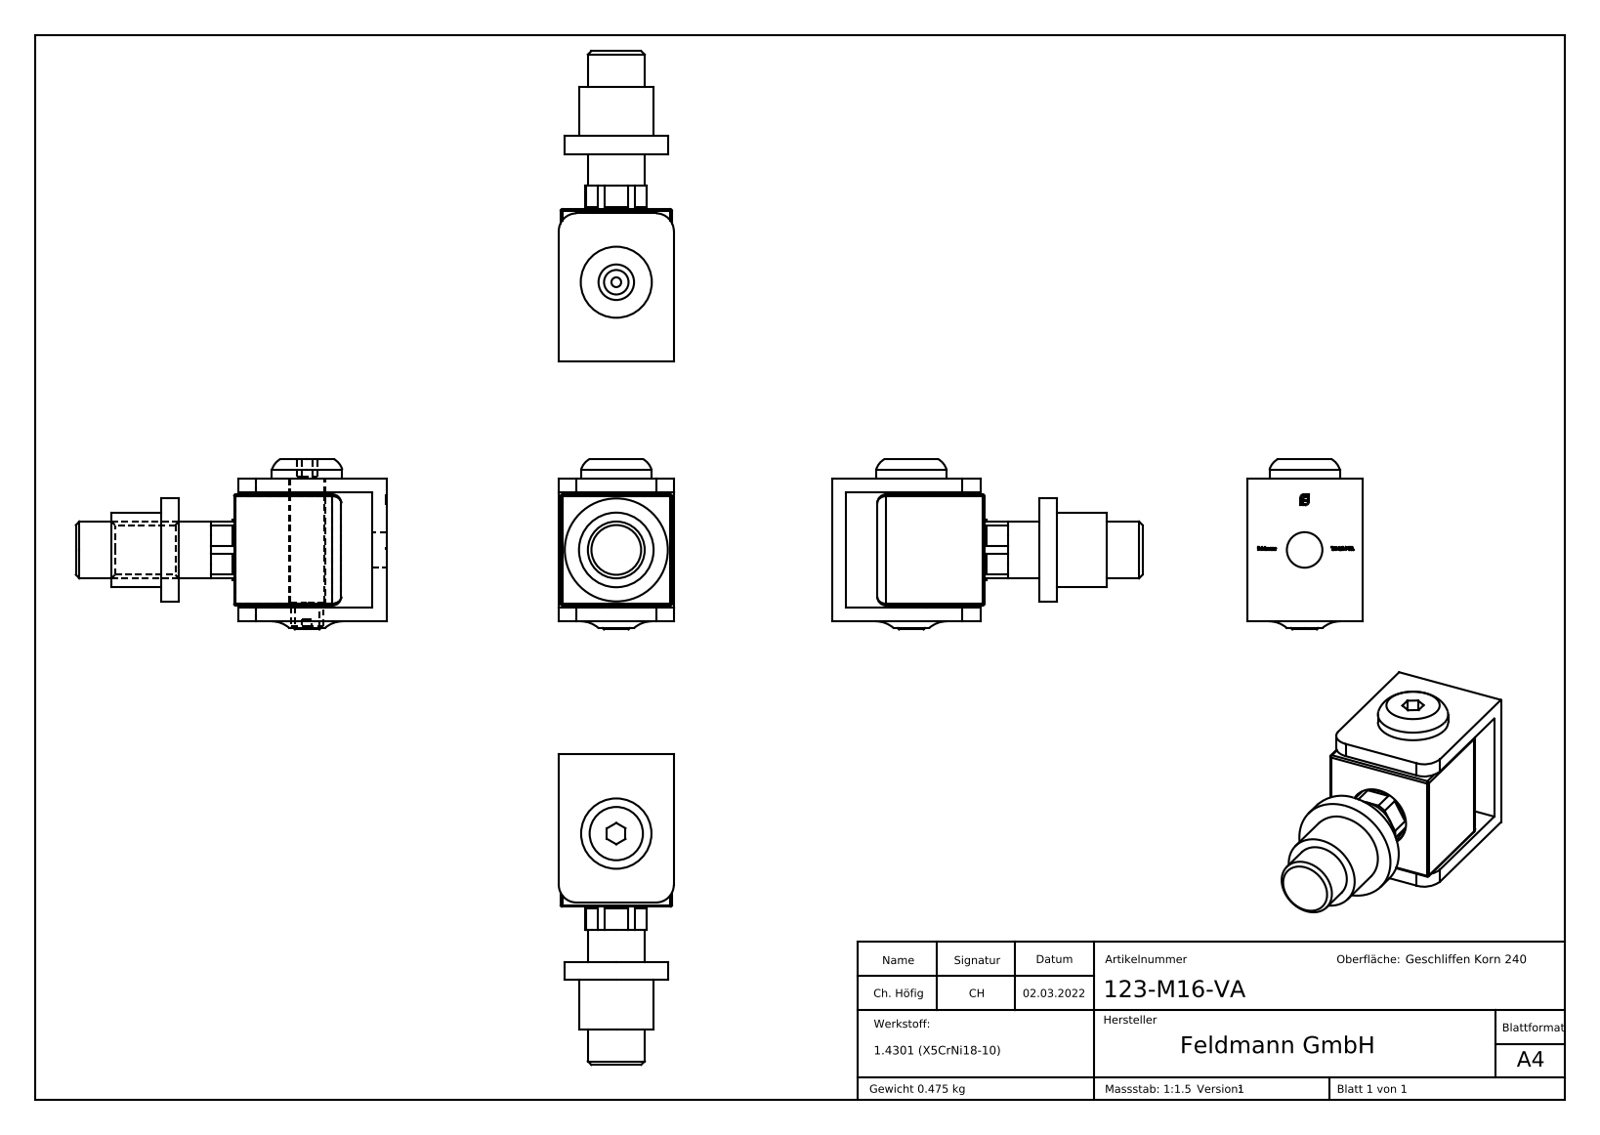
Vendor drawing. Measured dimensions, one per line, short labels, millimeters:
name: 123-MXX-VA Teil1_123-M16-VA Teil1; 123-M16-VA; 123-MXX-VA Teil2_123-M16-VA Teil2; 123-MXX-VA Teil4_123-M16-VA Teil4 (+1 more)
written by: SolidWorks 2018 (CONFIG_CONTROL_DESIGN)
unit: mm
bodies: 4 solids, 358 faces (216 planar, 29 cylindrical, 113 other)
size: 87.4 × 48 × 32.4
volume: 60 086 mm³; area: 22 661 mm²
holes: 2× ⌀10, 1× ⌀2.75, 1× ⌀6.8, 1× ⌀14
bosses: 1× ⌀29, 1× ⌀21, 1× ⌀19.8, 1× ⌀17.3, 1× ⌀16, 1× ⌀9.8, 1× ⌀8.9
rounds: 8× R0.5, 4× R2.5, 2× R5
face distances: 4, 36.2, 4.45, 35.75, 0.45, 31.75, 32.2, 40.2, 0.5, 31.9
